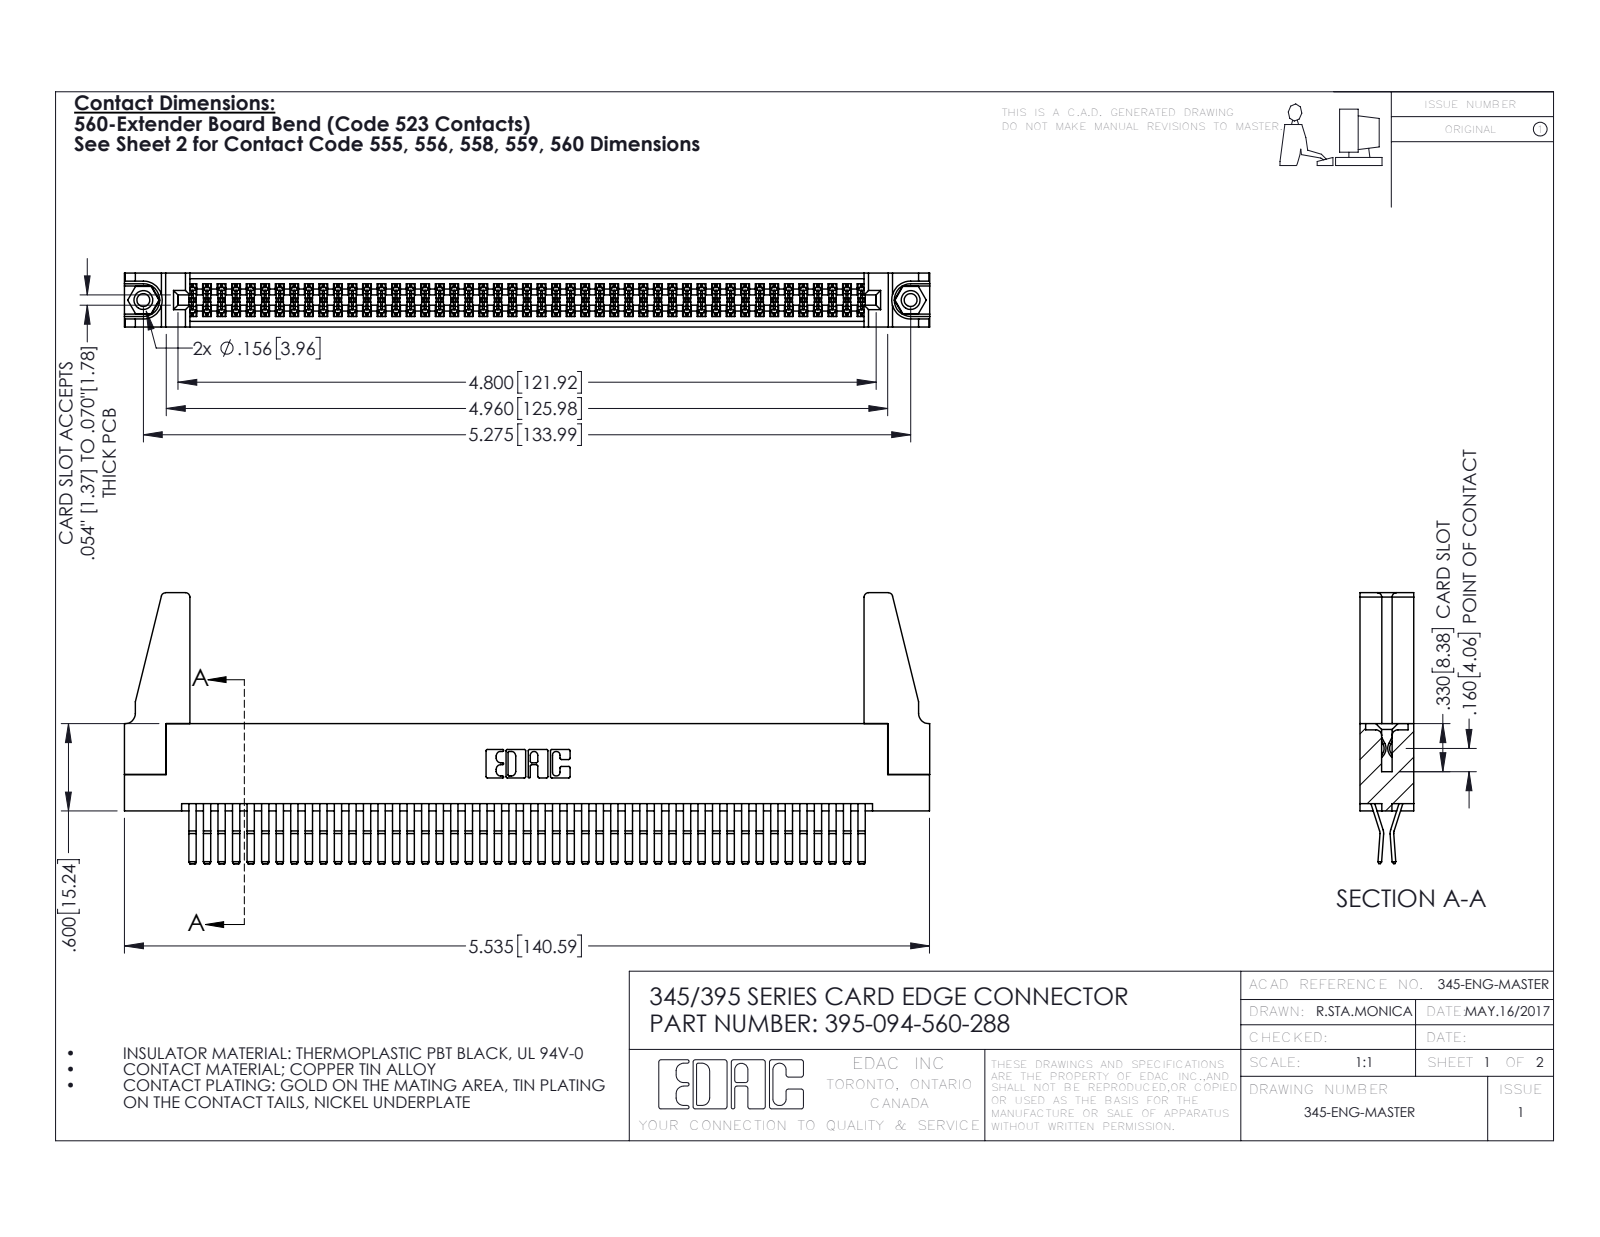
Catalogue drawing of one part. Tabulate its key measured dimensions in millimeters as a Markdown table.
| quantity | value |
| --- | --- |
| part name | 345-220-078_345-220-088; 395-094-560-288; 345 Part_Flush Mounting Lugs - 0.156 Dia-TH; 345-292-001_560 Tail (+1 more) |
| STEP written by | SolidWorks 2016 (CONFIG_CONTROL_DESIGN) |
| units | millimeters |
| bodies | 99 solids, 5138 faces (3254 planar, 1868 cylindrical, 16 other) |
| overall size | 140.6 × 47.3 × 9.4 |
| volume | 17 570 mm³ |
| surface area | 25 970 mm² |
| round holes (diameter × count) | 2.3 × 2, 3.2 × 2, 4 × 2, 1.6 × 1 |
| round bosses / shafts (diameter × count) | 3.9 × 2 |
| partial cylindrical surfaces (radius × count) | 0.2 × 141, 0.3 × 22, 0.8 × 8, 0.2 × 6, 0.8 × 6, 0.7 × 3, 0.3 × 2, 0.4 × 2 |
| main face-to-face distances | 1.8, 7.6, 0.6, 9.4, 5.1, 2.5, 6.9, 5.7, 4.4, 3.8 |
| hole center spacings | 6.9, 128, 134 |
